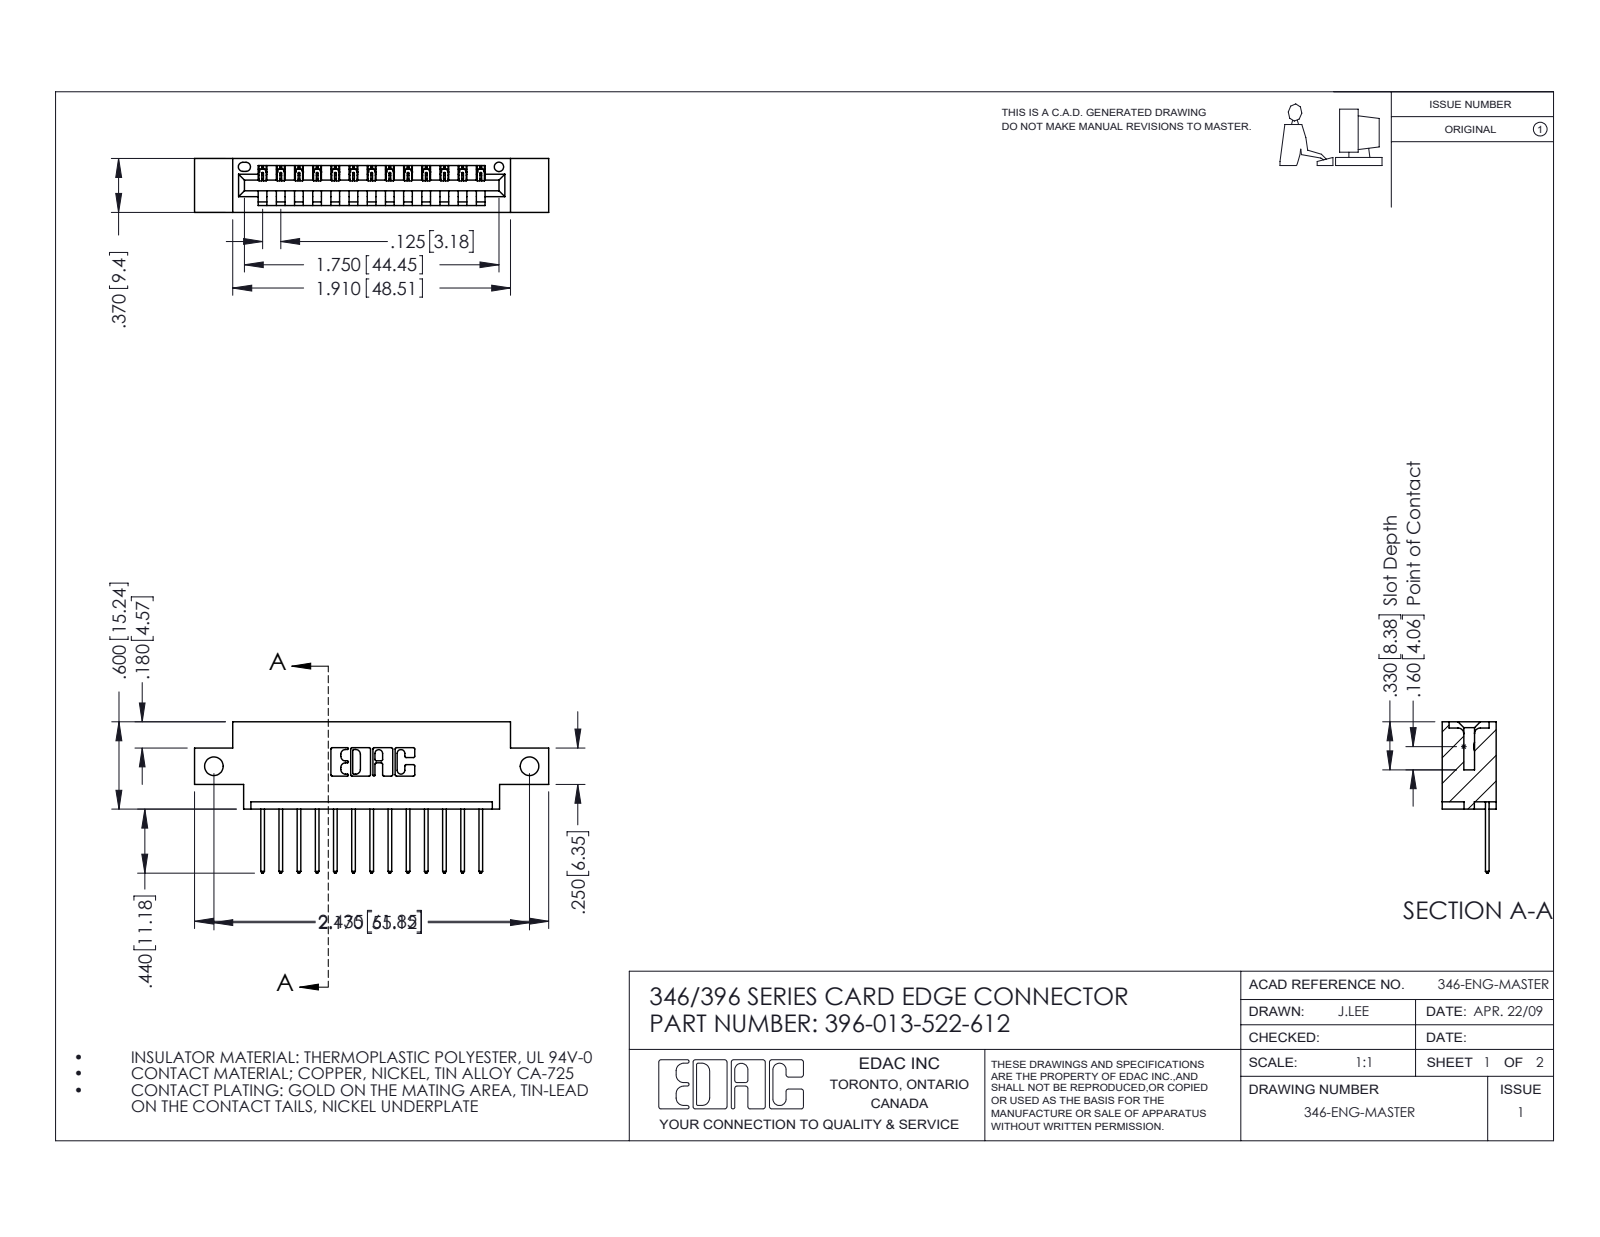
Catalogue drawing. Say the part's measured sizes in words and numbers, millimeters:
The part is named "396-013-522-612; 346 Part_0.170 Offset - Side Mount; 345-292-001_345-293-122". Its 3-D file was written by "SolidWorks 2016 (CONFIG_CONTROL_DESIGN)". It is 14 solids with 880 faces: 600 planar, 280 cylindrical and 0 other. Overall it measures 61.8 by 26.4 by 9.4 millimeters. Its volume is 5 470 cubic millimeters and its surface area 6 600 square millimeters. Round holes: 2 of diameter 3.3, 1 of diameter 1.6. Partial cylindrical surfaces (rounded edges, fillets, slot ends): 26 of radius 0.2, 26 of radius 0.3, 22 of radius 0.3, 6 of radius 0.2, 6 of radius 0.8, 3 of radius 0.7, 2 of radius 0.8, 2 of radius 1. The main face-to-face distances are 6.4, 9.4, 1.2, 8.2, 1.8, 7.6, 0.6, 3.8, 5.6, 2.5. The hole center spacings are 55.1.
